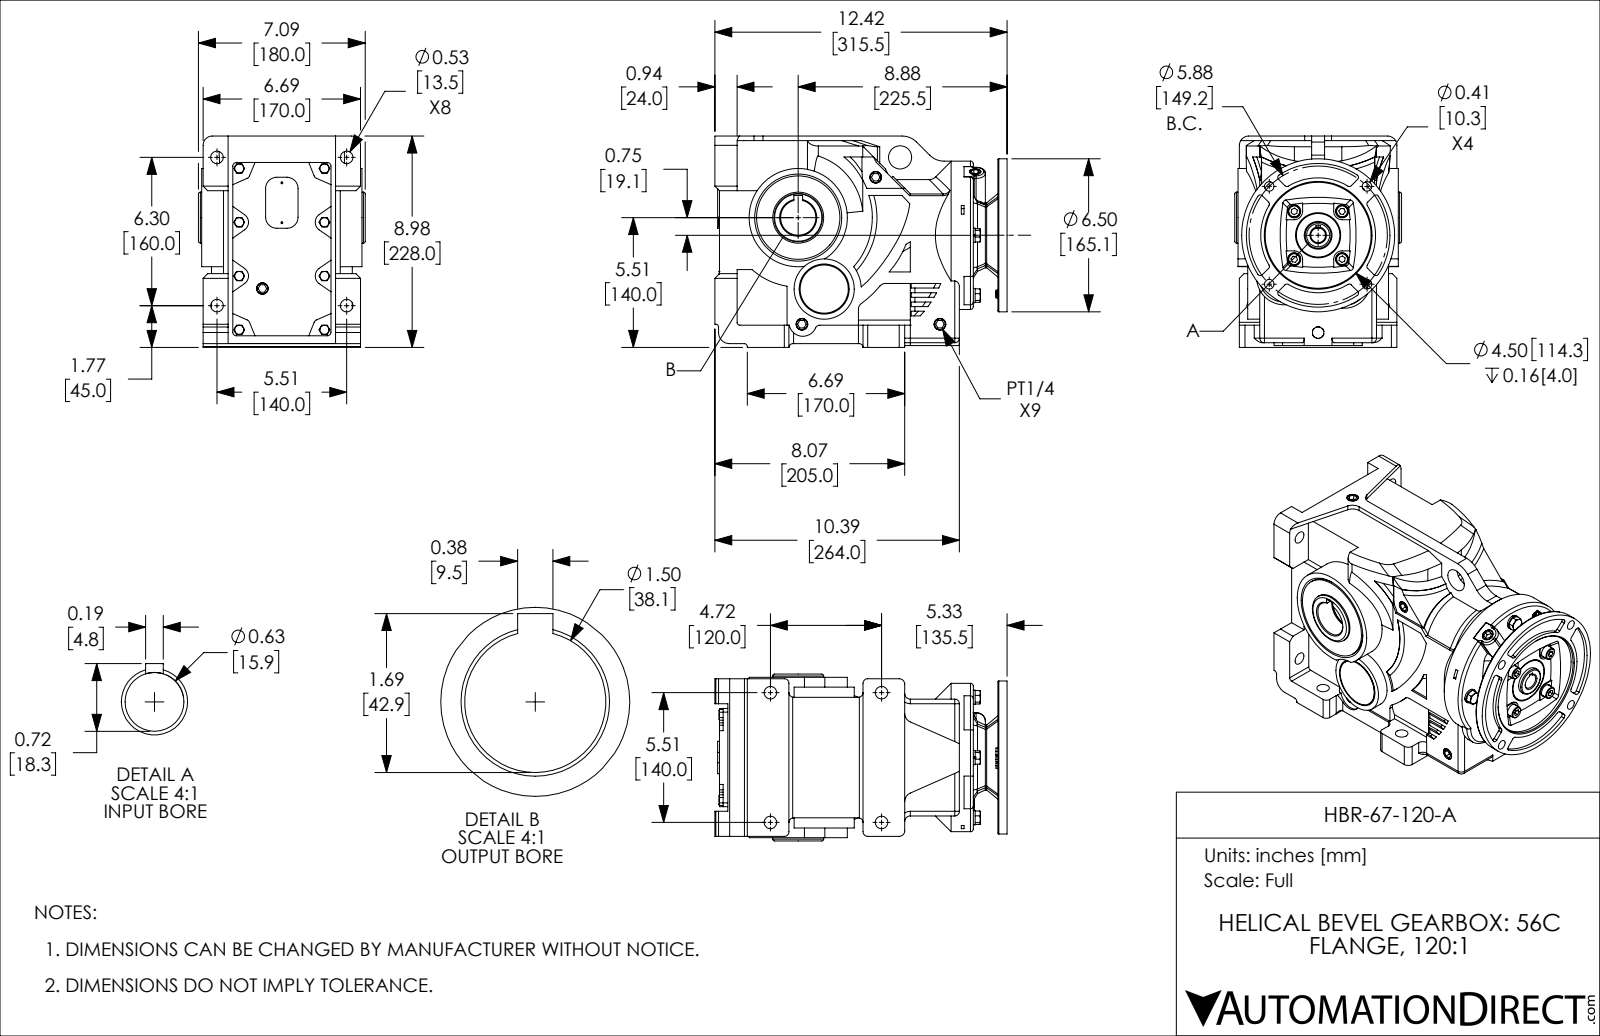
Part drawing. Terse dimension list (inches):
name: HBR-67-120-A
written by: SolidWorks 2018 (AUTOMOTIVE_DESIGN)
unit: in
bodies: 1 solid, 1106 faces (550 planar, 274 cylindrical, 282 other)
size: 12.421 × 8.976 × 7.087
volume: 473.6 in³; area: 628.4 in²
holes: 8× ⌀0.531, 4× ⌀0.323, 4× ⌀0.354, 4× ⌀0.406, 4× ⌀0.551, 2× ⌀0.079, 1× ⌀0.625, 1× ⌀0.846, 1× ⌀0.984, 1× ⌀1.5, 1× ⌀1.575, 1× ⌀4.5
bosses: 4× ⌀0.606, 4× ⌀0.512, 4× ⌀0.315, 1× ⌀6.5, 1× ⌀6.299, 1× ⌀4.173, 1× ⌀3.543, 1× ⌀2.559
rounds: 23× R0.118, 20× R0.197, 13× R0.394, 9× R0.079, 6× R0.157, 5× R0.472, 4× R0.236, 4× R0.354
face distances: 0.197, 0.079, 0.157, 0.945, 8.78, 0.059, 4.961, 11.831, 0.118, 0.591
hole spacings: 1.848, 2.132, 1.5, 2.559, 2.937, 3.27, 3.27, 3.619
